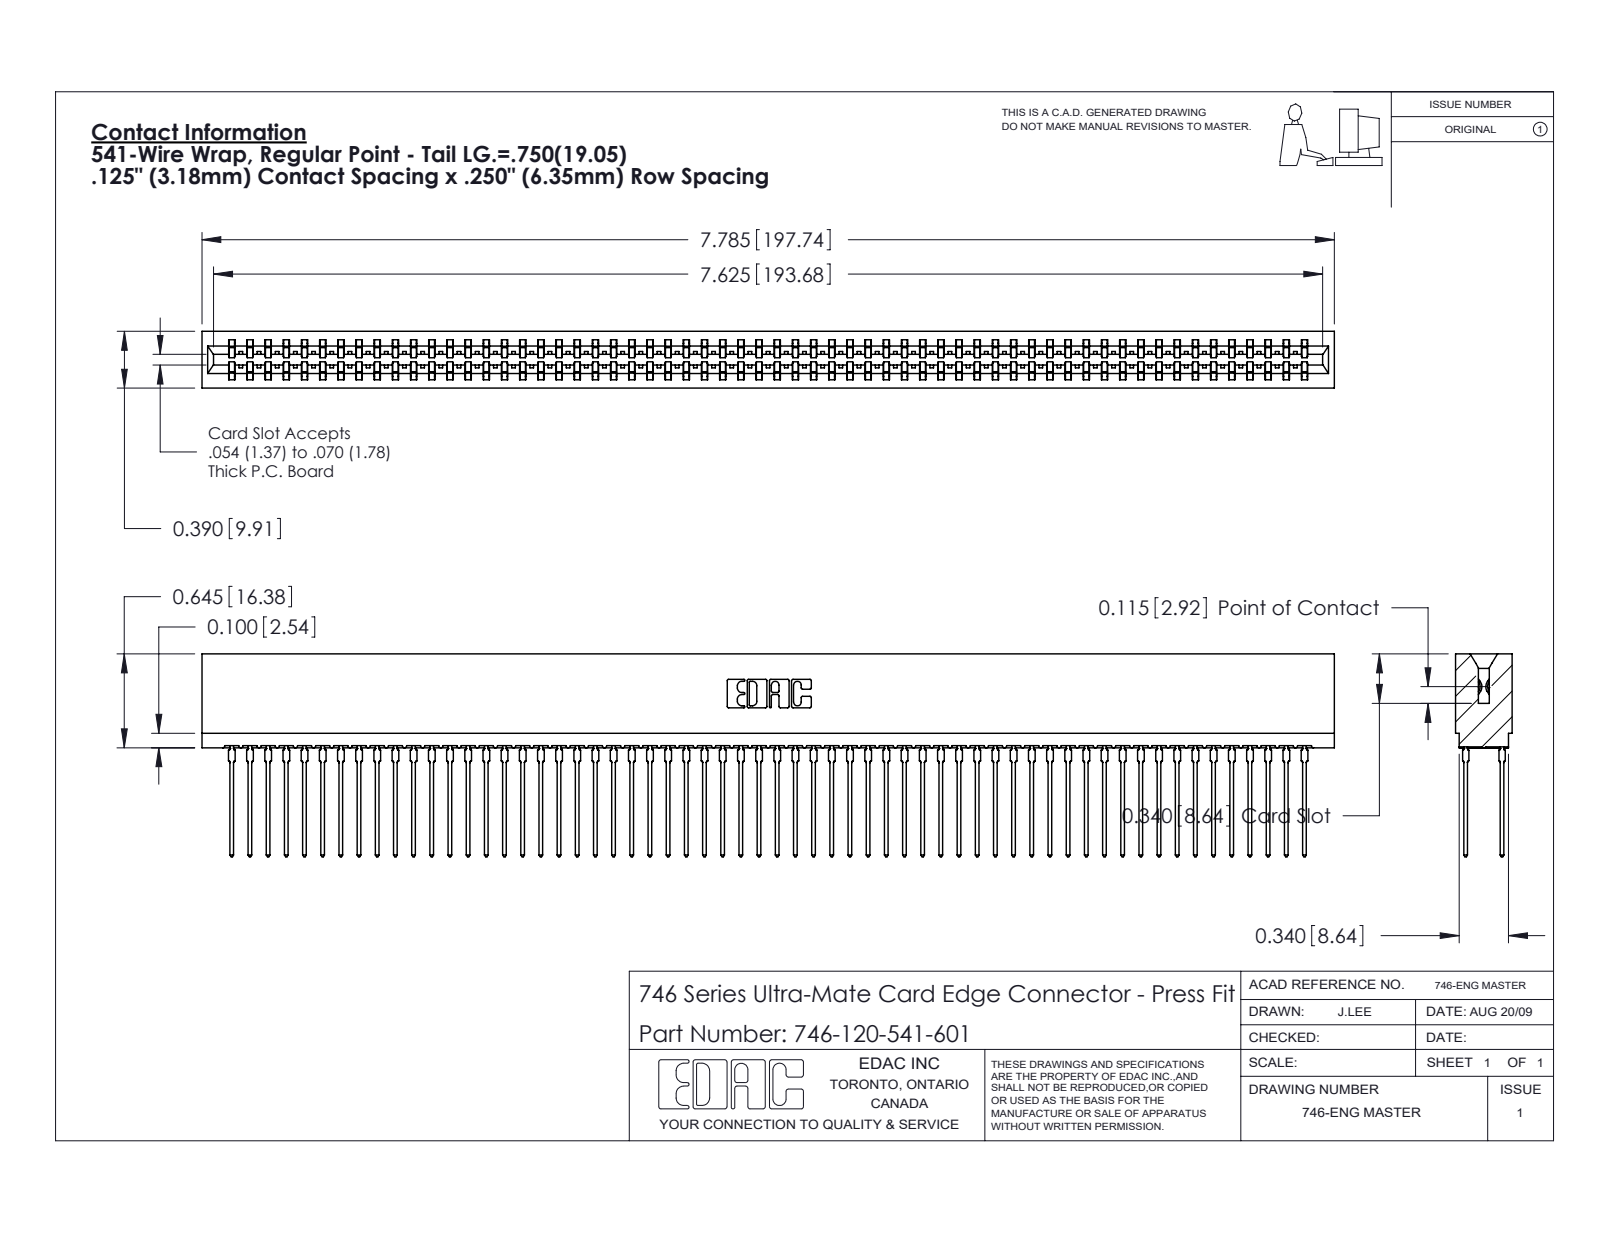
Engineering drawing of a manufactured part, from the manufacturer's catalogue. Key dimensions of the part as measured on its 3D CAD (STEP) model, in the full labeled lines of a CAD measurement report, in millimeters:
Part name (STEP PRODUCT): 746-292-001_541; 746-120-541-601; 746 Part_.340 Slot Depth - 01
STEP written by: SolidWorks 2020 (CONFIG_CONTROL_DESIGN)
Units: millimetres
Bodies: 121 solids, 10837 faces (5575 planar, 2142 cylindrical, 3120 other)
Overall size (bounding box): 197.7 × 35.4 × 9.9
Volume: 23 290 mm³ · Surface area: 37 650 mm²
Partial cylindrical surfaces — rounded edges, fillets, slot ends (radius × count): R0.5 ×240, R0.4 ×61, R0.3 ×22, R0.1 ×8, R0.3 ×8, R0.2 ×6, R0.8 ×6, R0.7 ×3
Main face-to-face distances: 1.4, 8.5, 0.6, 6.4, 7.8, 9.9, 2.1, 7, 5.7, 0.4
